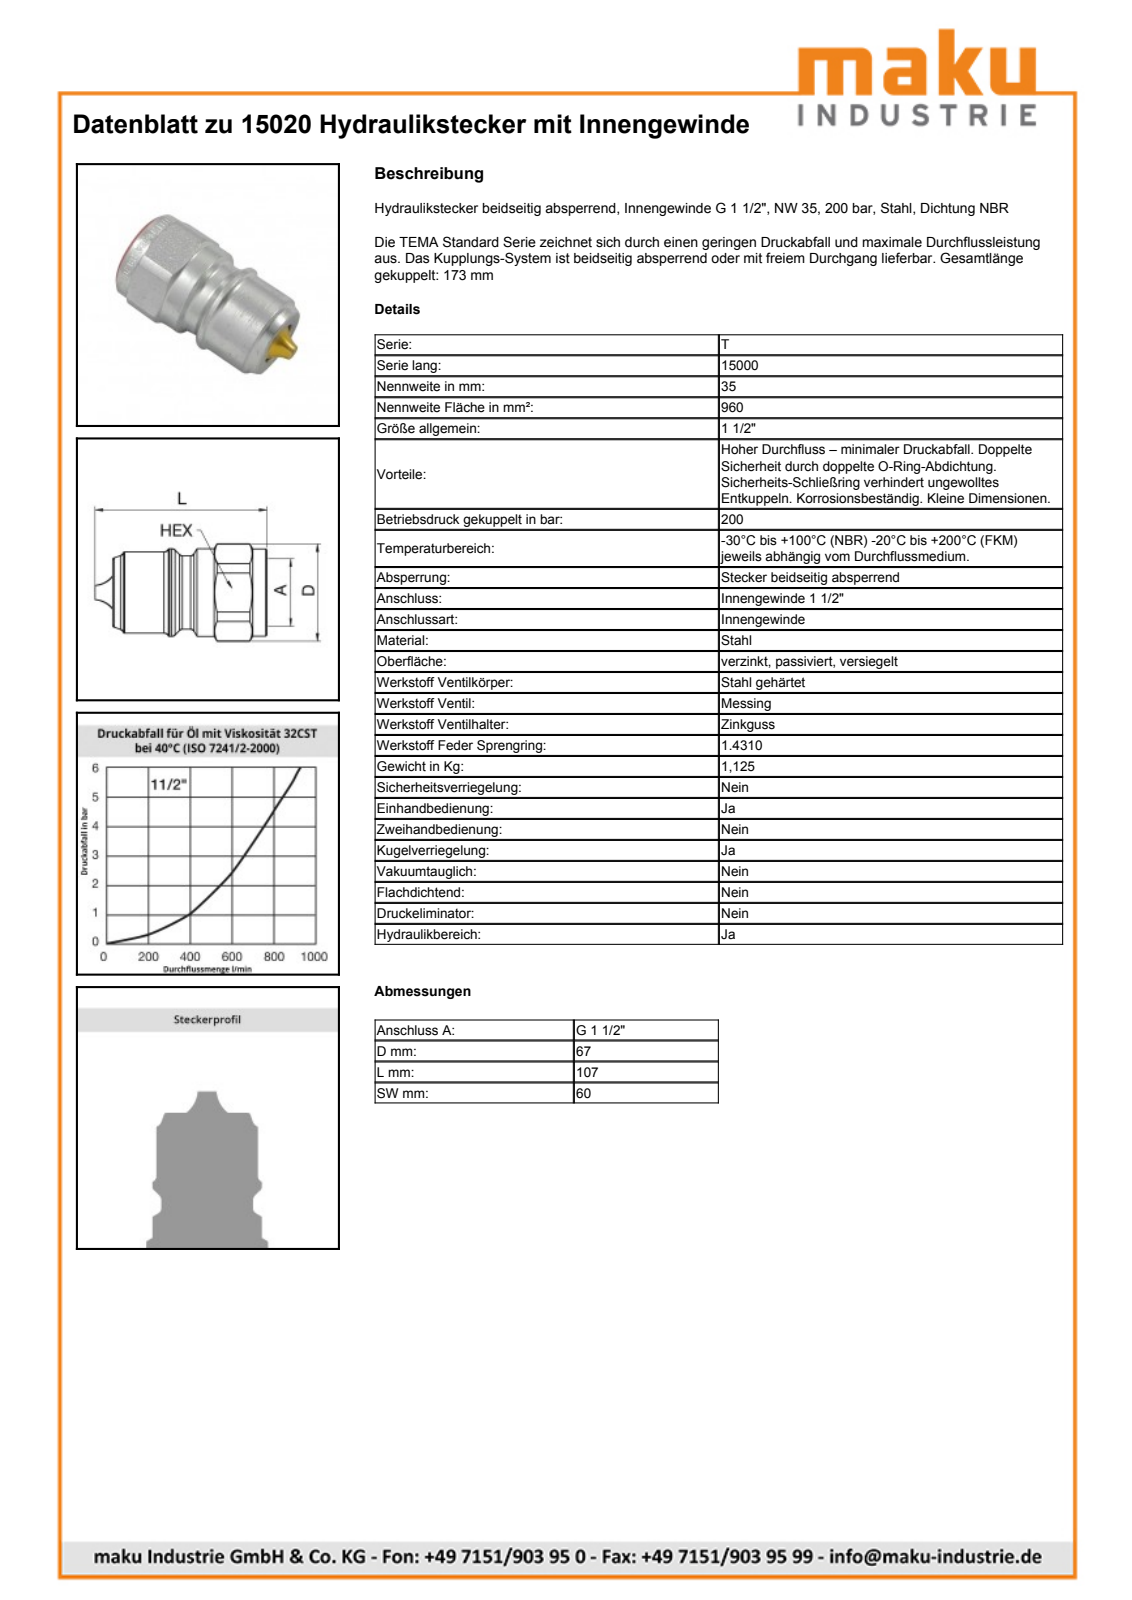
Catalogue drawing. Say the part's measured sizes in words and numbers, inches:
The part is named "15020". Its 3-D file was written by "SolidWorks 2009 (AUTOMOTIVE_DESIGN)". It is 1 solid with 68 faces: 18 planar, 16 cylindrical and 34 other. Overall it measures 4.213 by 2.638 by 2.638 inches. Its volume is 11.75 cubic inches and its surface area 54.05 square inches. Round holes: 1 of diameter 1.378, 1 of diameter 1.496, 1 of diameter 1.765. Round bosses or shafts: 1 of diameter 2.638, 1 of diameter 2.016, 1 of diameter 1.921, 1 of diameter 1.781. The main face-to-face distances are 2.362, 0.984, 1.203, 2.187, 0.175, 1.378, 1.85, 2.025, 3.228, 4.213.
